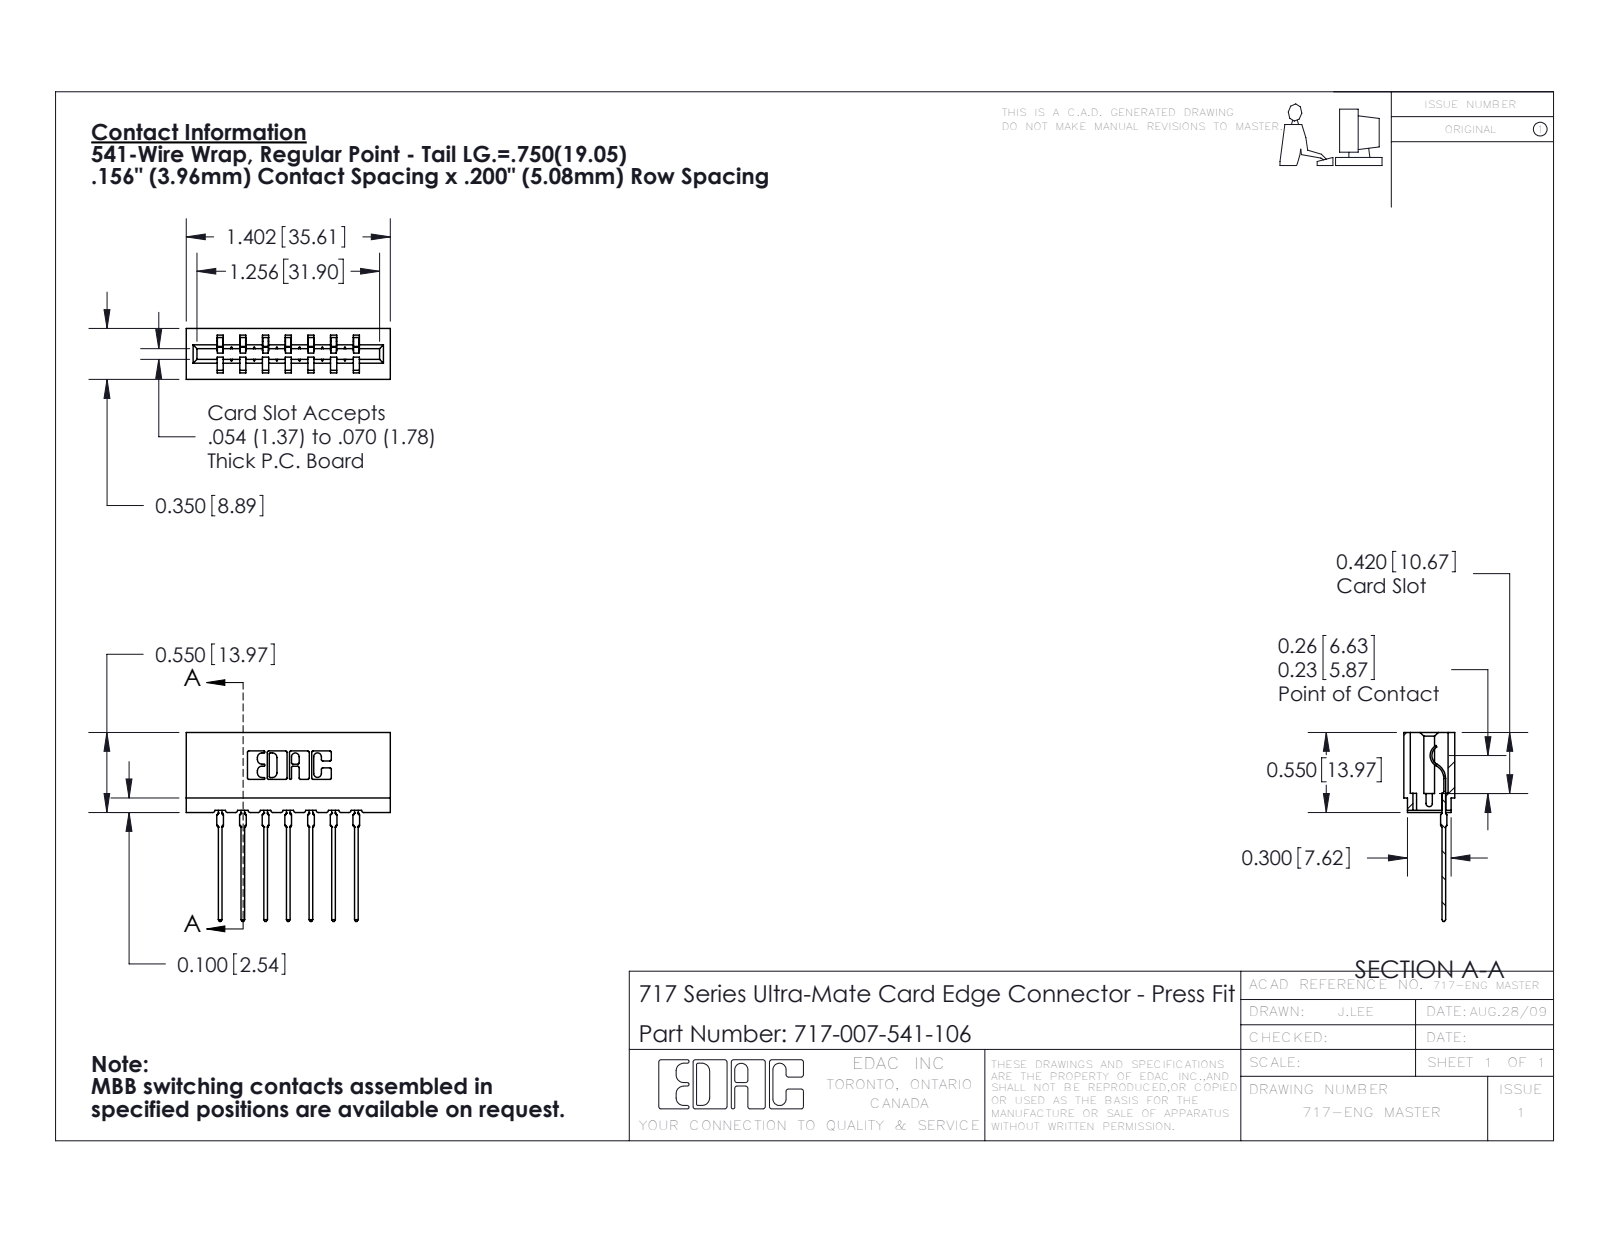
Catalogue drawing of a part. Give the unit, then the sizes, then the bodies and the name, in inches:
Units: inches
Overall size (bounding box): 1.402 × 1.299 × 0.35
Partial cylindrical surfaces — rounded edges, fillets, slot ends (radius × count): R0.01 ×22, R0.015 ×14, R0.021 ×14, R0.007 ×6, R0.031 ×6, R0.005 ×4, R0.011 ×4, R0.026 ×3
Main face-to-face distances: 0.212, 0.156, 0.138, 0.35, 0.198, 0.312, 0.468, 0.624, 0.042, 0.27
Volume: 0.195 in³ · Surface area: 6.597 in²
Bodies: 8 solids, 885 faces (530 planar, 173 cylindrical, 182 other)
Part name (STEP PRODUCT): 745-292-001_541; 717-007-541-106; 717 Part_Insulator Option - 06
STEP written by: SolidWorks 2016 (CONFIG_CONTROL_DESIGN)
